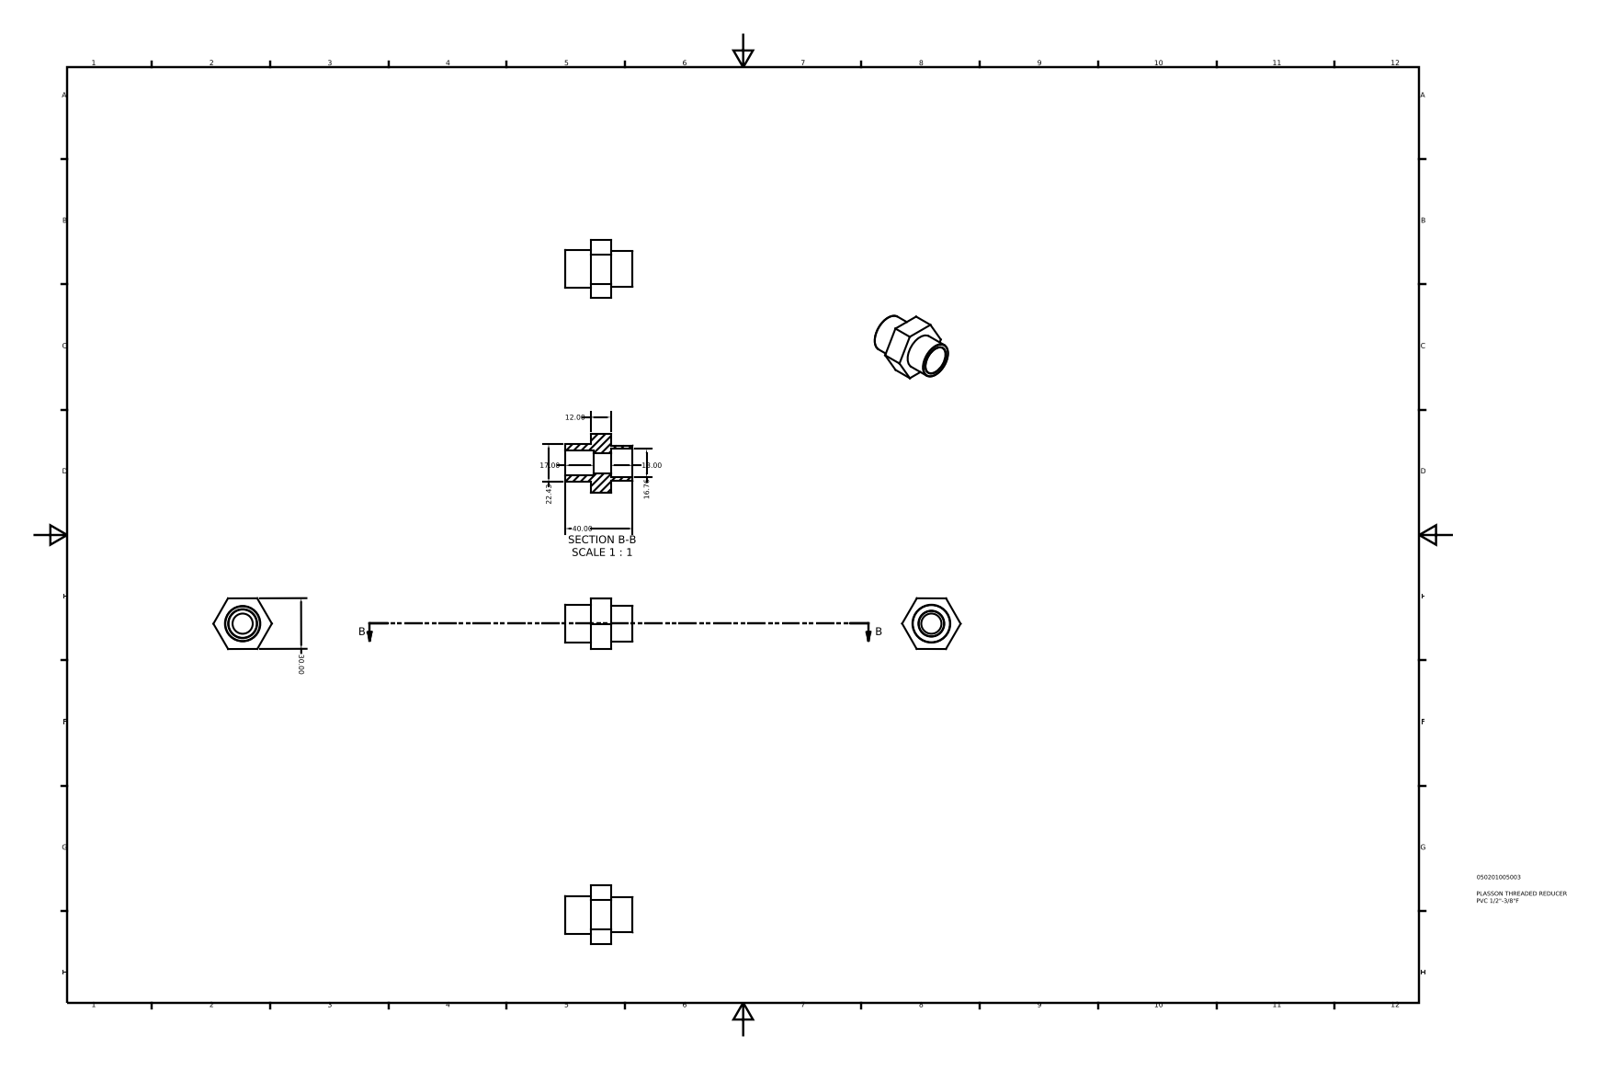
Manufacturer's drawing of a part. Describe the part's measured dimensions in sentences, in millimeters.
The part is named "050201005003". Its 3-D file was written by "Autodesk Inventor 2015 (AUTOMOTIVE_DESIGN)". It is 1 solid with 21 faces: 12 planar, 5 cylindrical and 4 other. Overall it measures 40 by 34.64 by 30.05 millimeters. Its volume is 12 782 cubic millimeters and its surface area 6 331 square millimeters. Round holes: 1 of diameter 11.96, 1 of diameter 14.95, 1 of diameter 16.76. Round bosses or shafts: 1 of diameter 22.43, 1 of diameter 20.95. The main face-to-face distances are 30.02, 12, 30, 15, 27, 40, 25, 13, 17, 2.
